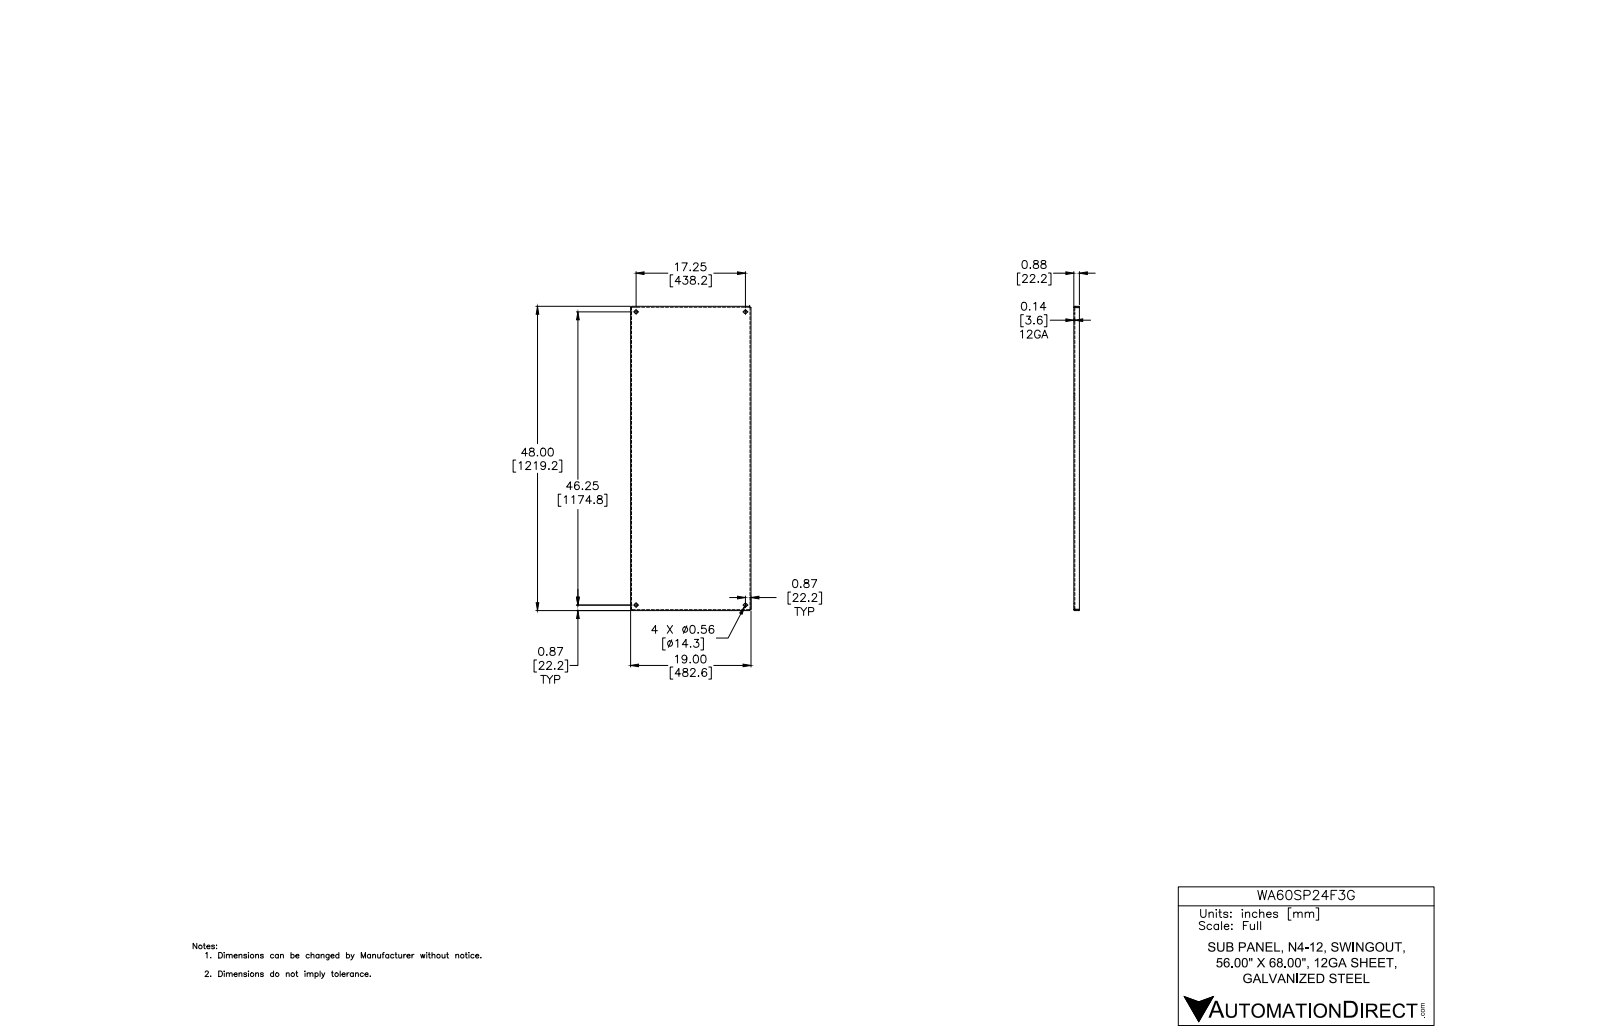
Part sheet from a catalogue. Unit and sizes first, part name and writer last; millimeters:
Units: millimetres
Overall size (bounding box): 1219.2 × 482.6 × 22.2
Round holes (diameter × count): ⌀14.3 ×4
Partial cylindrical surfaces — rounded edges, fillets, slot ends (radius × count): R0.8 ×4, R3.2 ×4
Main face-to-face distances: 2.4, 480.2, 477.9, 482.6, 1216.8, 1214.5, 1219.2, 19.8, 22.2, 4.1
Hole centre spacings: 438.2, 1174.8, 1253.8
Volume: 1 552 000 mm³ · Surface area: 1 312 000 mm²
Bodies: 1 solid, 42 faces (22 planar, 12 cylindrical, 8 other)
Part name (STEP PRODUCT): WA60SP24F3G-WA90SP36F4G
STEP written by: Autodesk Inventor 2012 (AUTOMOTIVE_DESIGN)
